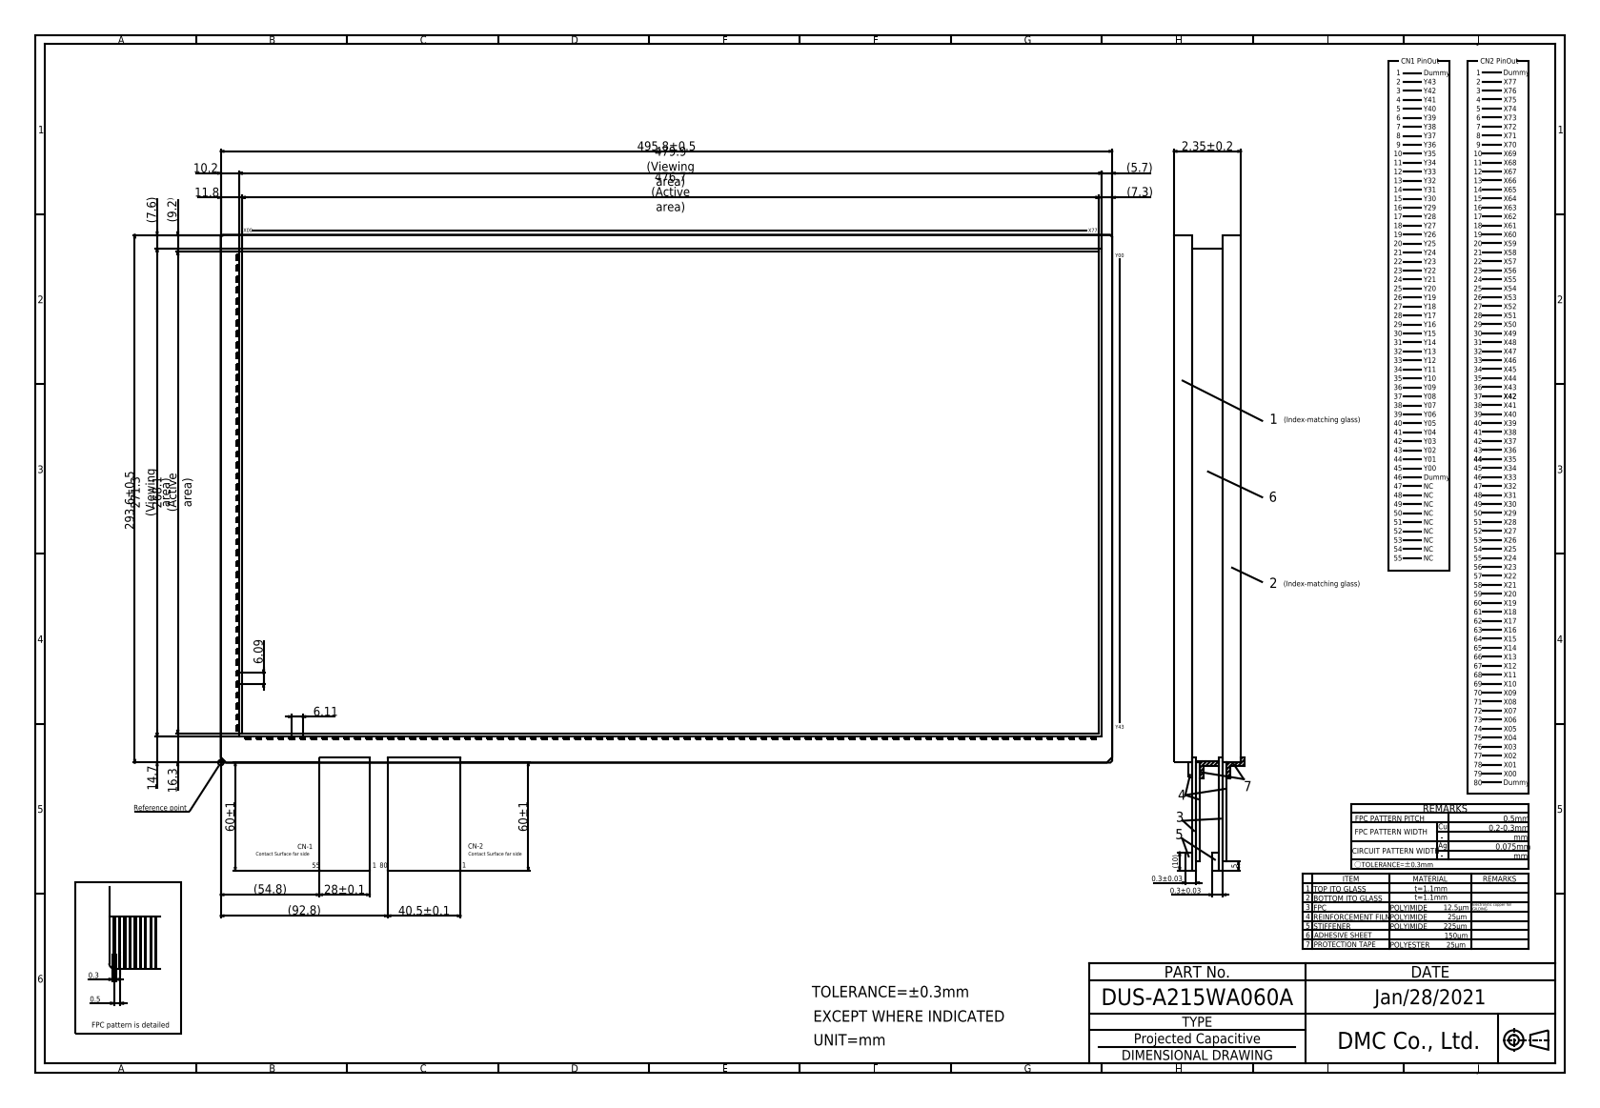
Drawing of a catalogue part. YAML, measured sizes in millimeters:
part_name: "DUS-A215WA060A"
step_written_by: "Autodesk Inventor 2020 (CONFIG_CONTROL_DESIGN)"
units: millimeters
bodies: {solids: 1, faces: 578, planar: 574, cylindrical: 4, other: 0}
overall_size: [694.12, 412.32, 2.35]
volume: 342424
surface_area: 303451
partial_cylinders:
  - {radius: 0.2, count: 4}
face_to_face_distances: [2.35, 1.1, 1.2, 1.15, 1.25, 1, 2.25, 293.6, 495.8, 0.8]
